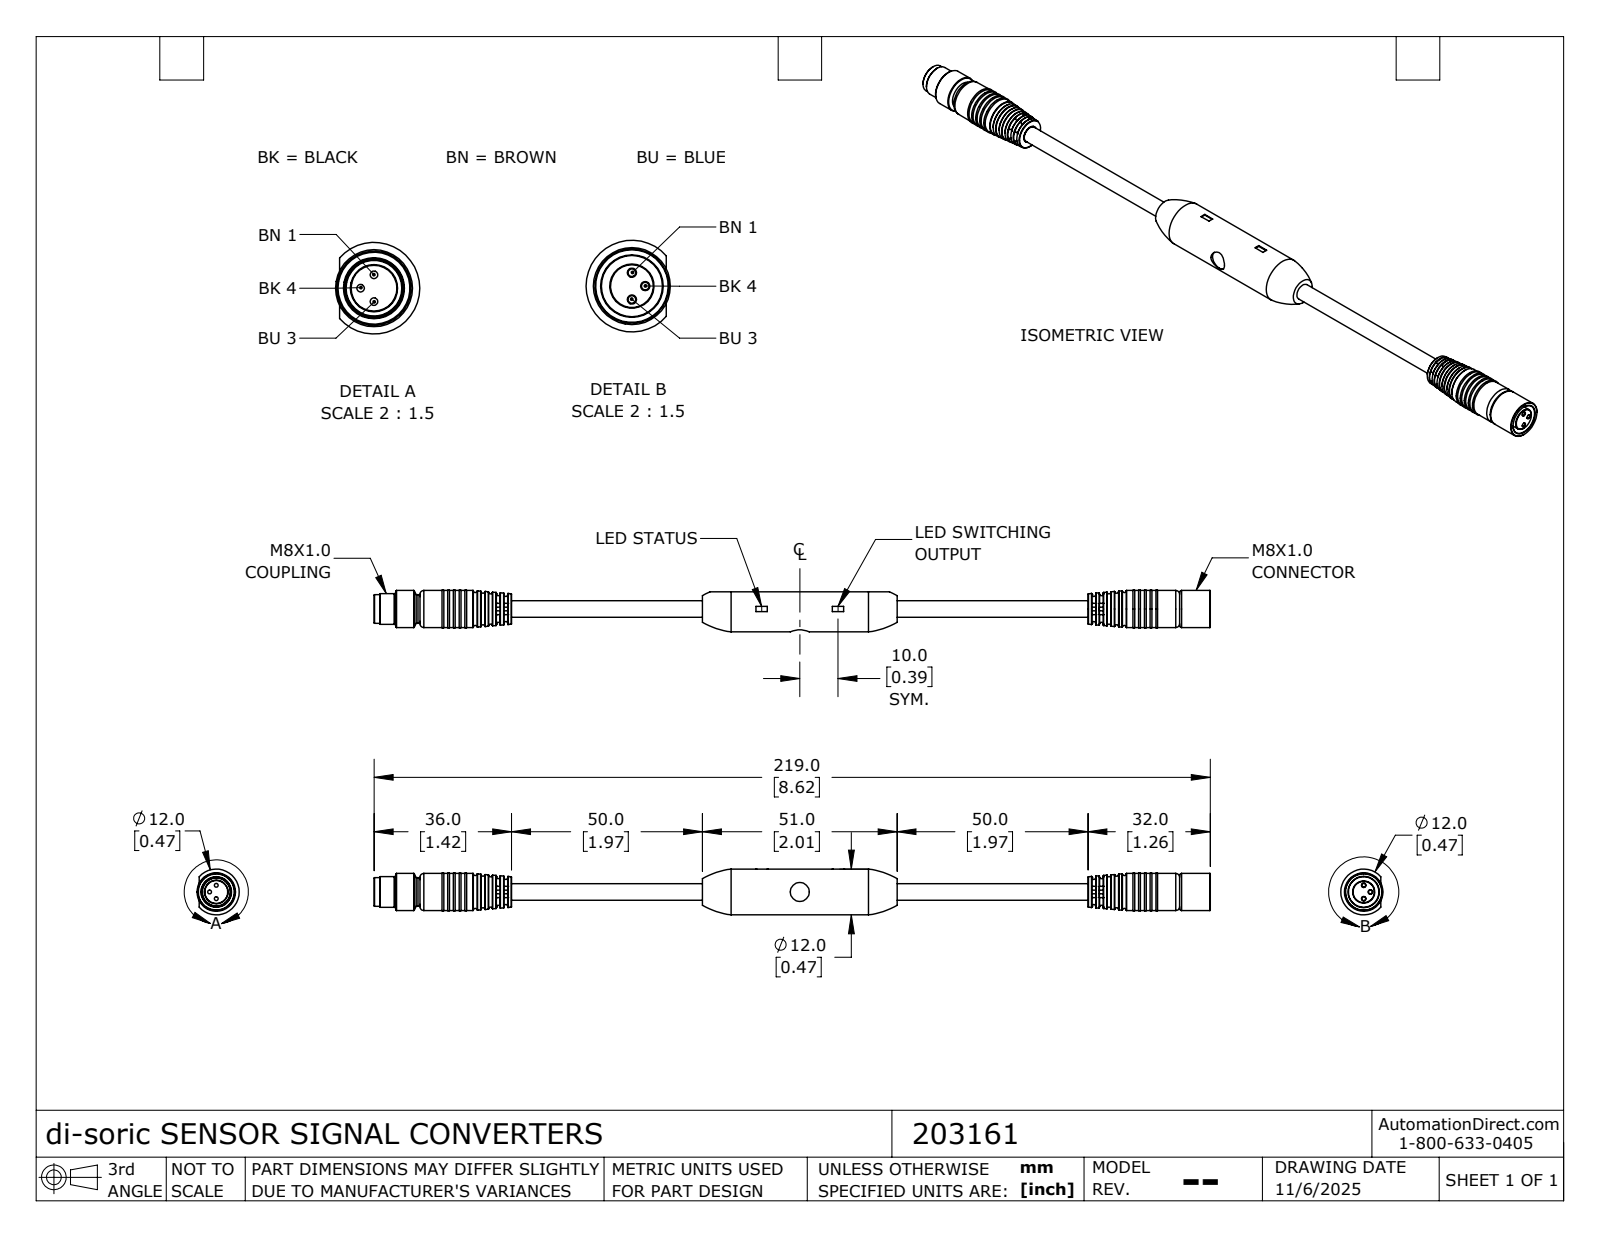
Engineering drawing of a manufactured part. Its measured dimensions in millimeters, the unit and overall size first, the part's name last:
Units: millimetres
Overall size (bounding box): 219 × 12 × 12
Round holes (diameter × count): ⌀1 ×3, ⌀1.43 ×3, ⌀1.72 ×3, ⌀3 ×1, ⌀4.6 ×1, ⌀5 ×1, ⌀6 ×1, ⌀8 ×1
Round bosses / shafts (diameter × count): ⌀9.7 ×1, ⌀7.9 ×1, ⌀7.5 ×1, ⌀5.8 ×1, ⌀4.5 ×1, ⌀4.3 ×1
Partial cylindrical surfaces — rounded edges, fillets, slot ends (radius × count): R6 ×1
Main face-to-face distances: 1, 2, 3, 155, 154, 156, 51, 157, 153, 6
Hole centre spacings: 1.6, 0.84, 1, 1.46, 1.75, 1.01, 1.1, 1.73
Volume: 10 010 mm³ · Surface area: 7 758 mm²
Bodies: 1 solid, 260 faces (132 planar, 42 cylindrical, 86 other)
Part name (STEP PRODUCT): TKHM-Z_TSM-Z_UN
STEP written by: SolidWorks 2024 (AUTOMOTIVE_DESIGN)
